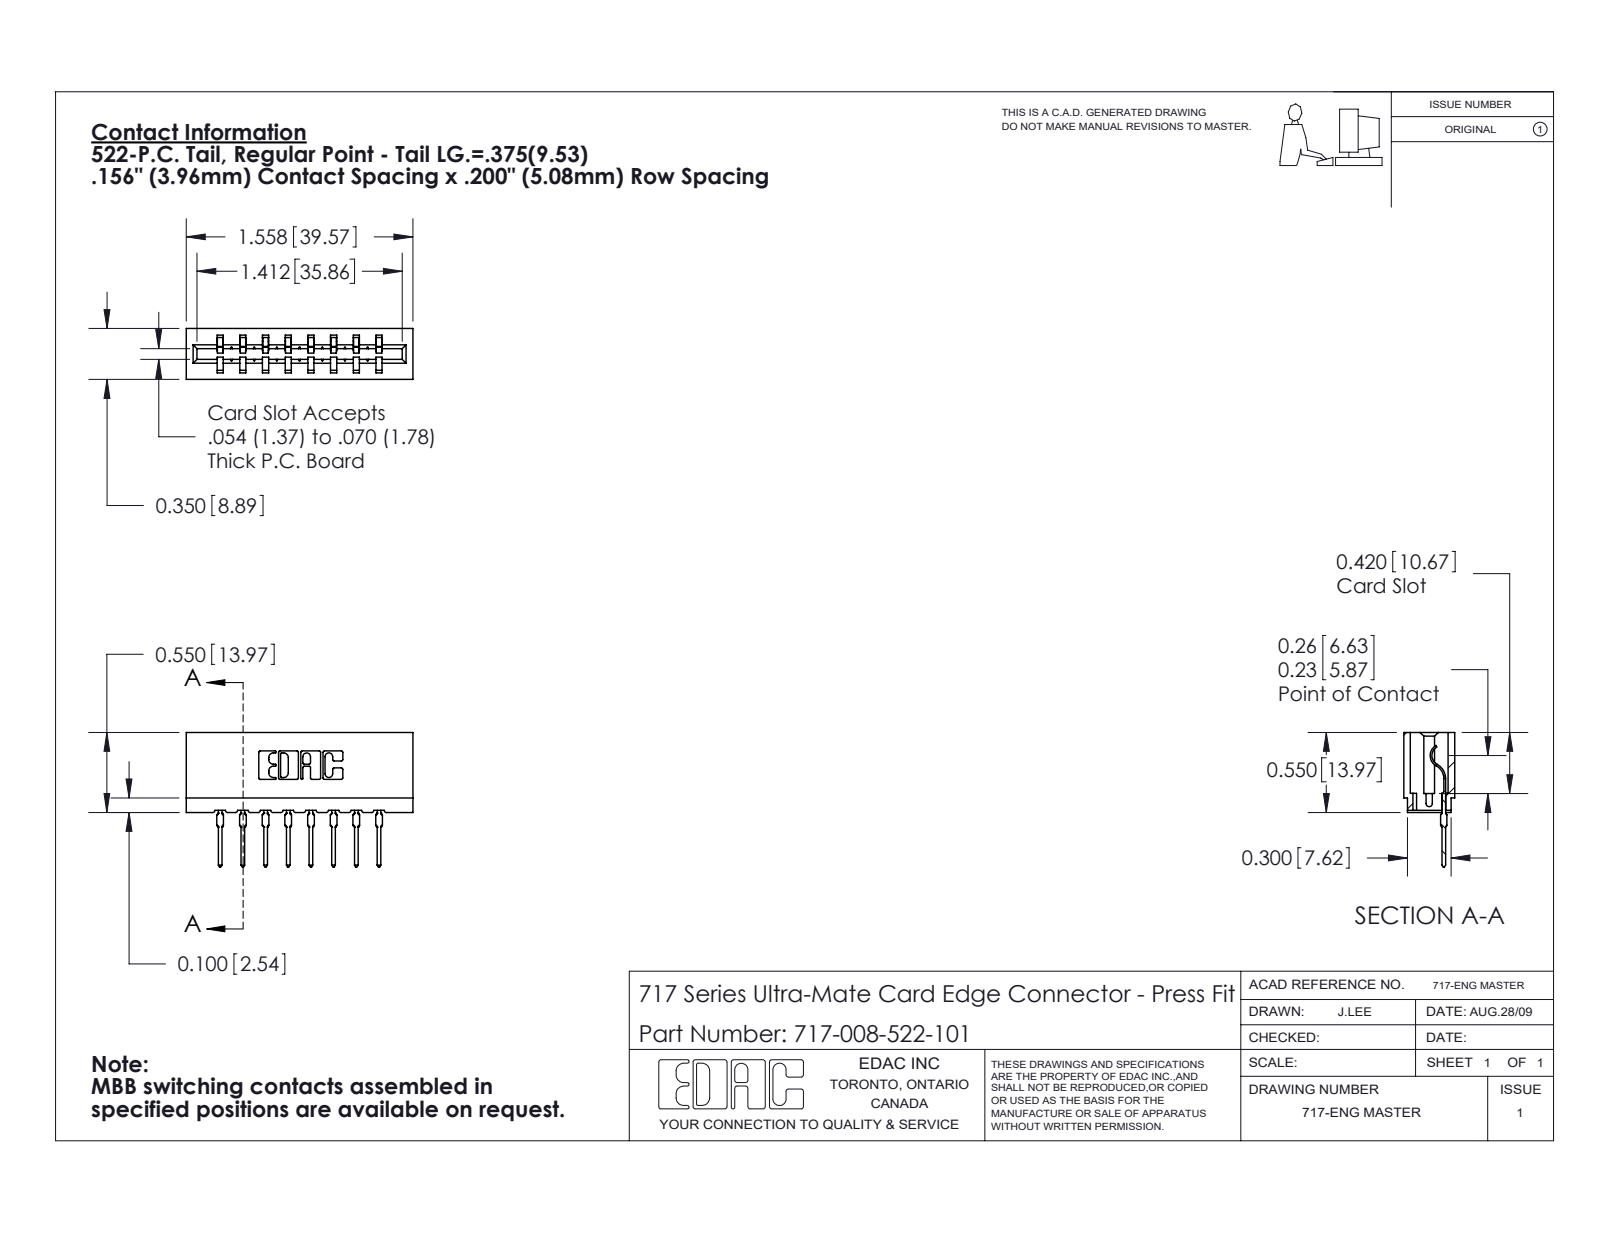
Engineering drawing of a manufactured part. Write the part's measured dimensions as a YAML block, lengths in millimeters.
part_name: "717-008-522-101; 745-292-001_522; 717 Part_Insulator Option - 06"
step_written_by: "SolidWorks 2020 (CONFIG_CONTROL_DESIGN)"
units: millimeters
bodies: {solids: 9, faces: 998, planar: 598, cylindrical: 192, other: 208}
overall_size: [39.6, 23.5, 8.9]
volume: 3510
surface_area: 4564
partial_cylinders:
  - {radius: 0.3, count: 22}
  - {radius: 0.4, count: 16}
  - {radius: 0.5, count: 16}
  - {radius: 0.2, count: 6}
  - {radius: 0.8, count: 6}
  - {radius: 0.1, count: 4}
  - {radius: 0.3, count: 4}
  - {radius: 0.7, count: 3}
face_to_face_distances: [5.4, 4, 3.5, 15.8, 11.9, 5, 7.9, 8.9, 1.1, 6.9]
